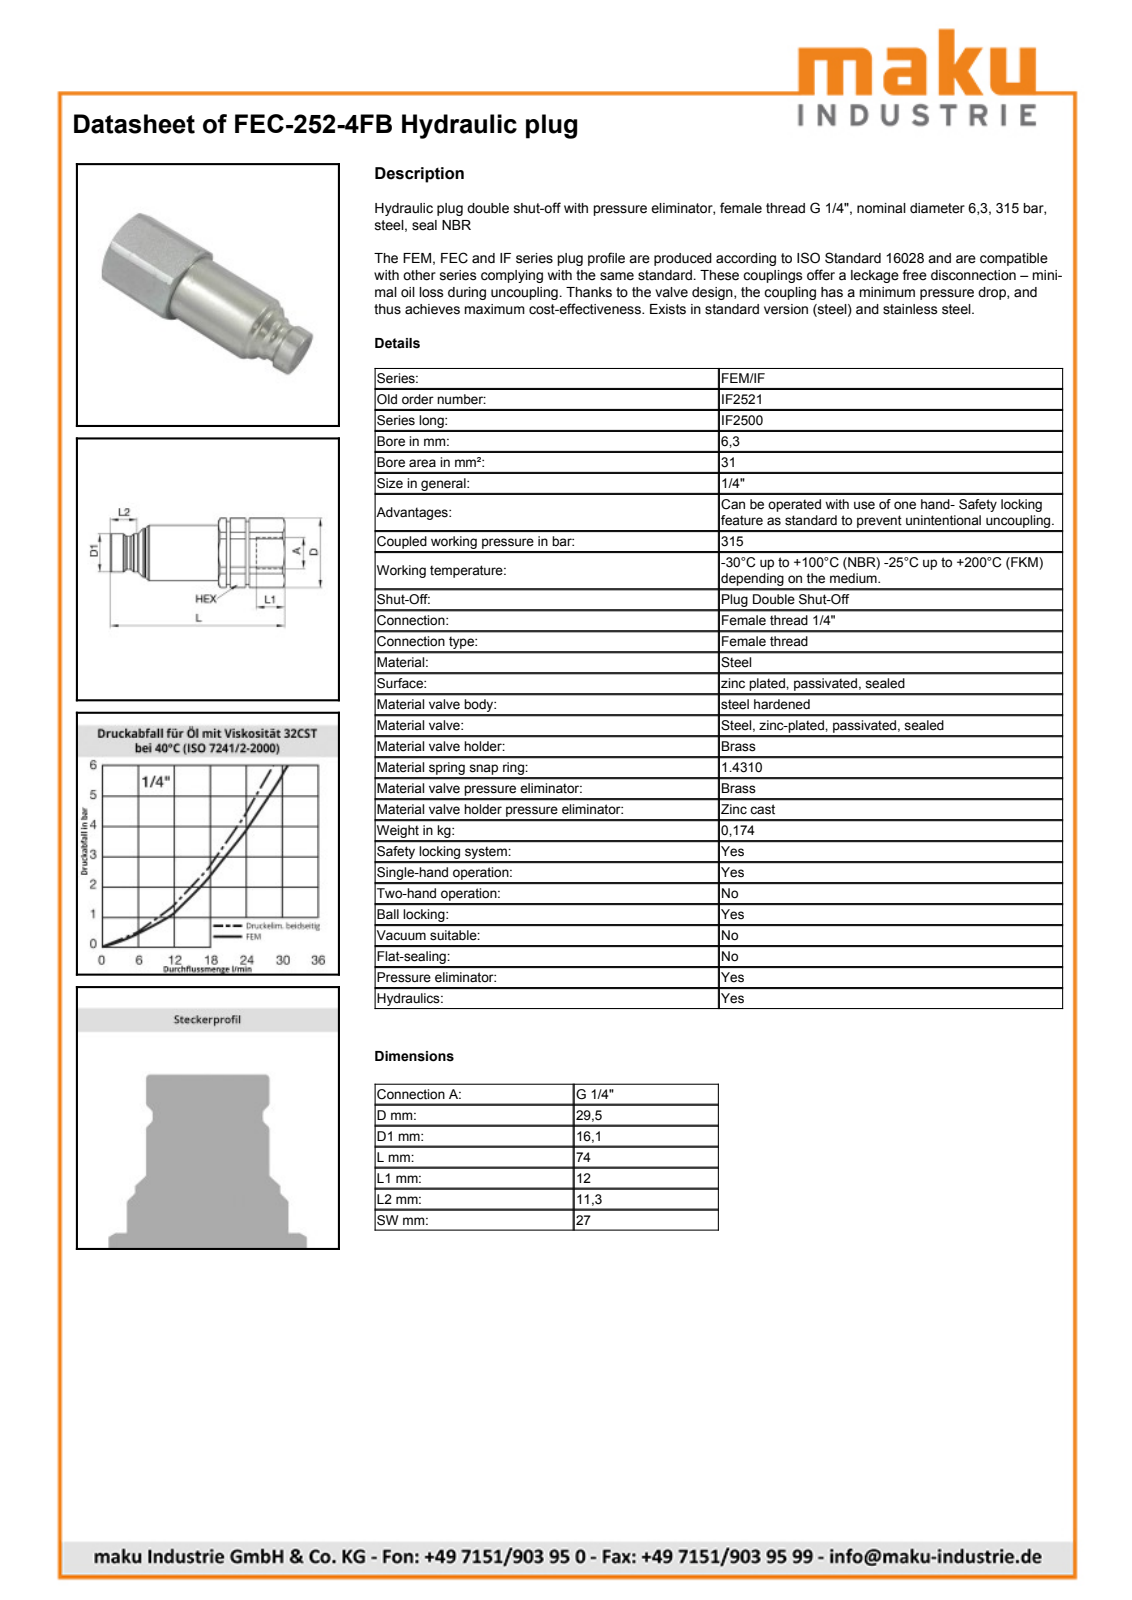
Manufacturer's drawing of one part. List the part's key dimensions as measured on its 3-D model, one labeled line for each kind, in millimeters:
Part name (STEP PRODUCT): FEC-252-4FB
STEP written by: SolidWorks 2009 (AUTOMOTIVE_DESIGN)
Units: millimetres
Bodies: 1 solid, 97 faces (13 planar, 28 cylindrical, 56 other)
Overall size (bounding box): 73.9 × 29.5 × 27
Volume: 32 413 mm³ · Surface area: 7 591 mm²
Round holes (diameter × count): ⌀9.7 ×1, ⌀11.5 ×1, ⌀20.92 ×1, ⌀22.2 ×1
Round bosses / shafts (diameter × count): ⌀23.5 ×1, ⌀20.75 ×1, ⌀20.7 ×1, ⌀16.15 ×1, ⌀13.95 ×1, ⌀9.6 ×1
Partial cylindrical surfaces — rounded edges, fillets, slot ends (radius × count): R14.75 ×1
Main face-to-face distances: 27, 28, 45.9, 73.9, 59.78, 13.88, 14.12, 45.8, 13.98, 28.1
